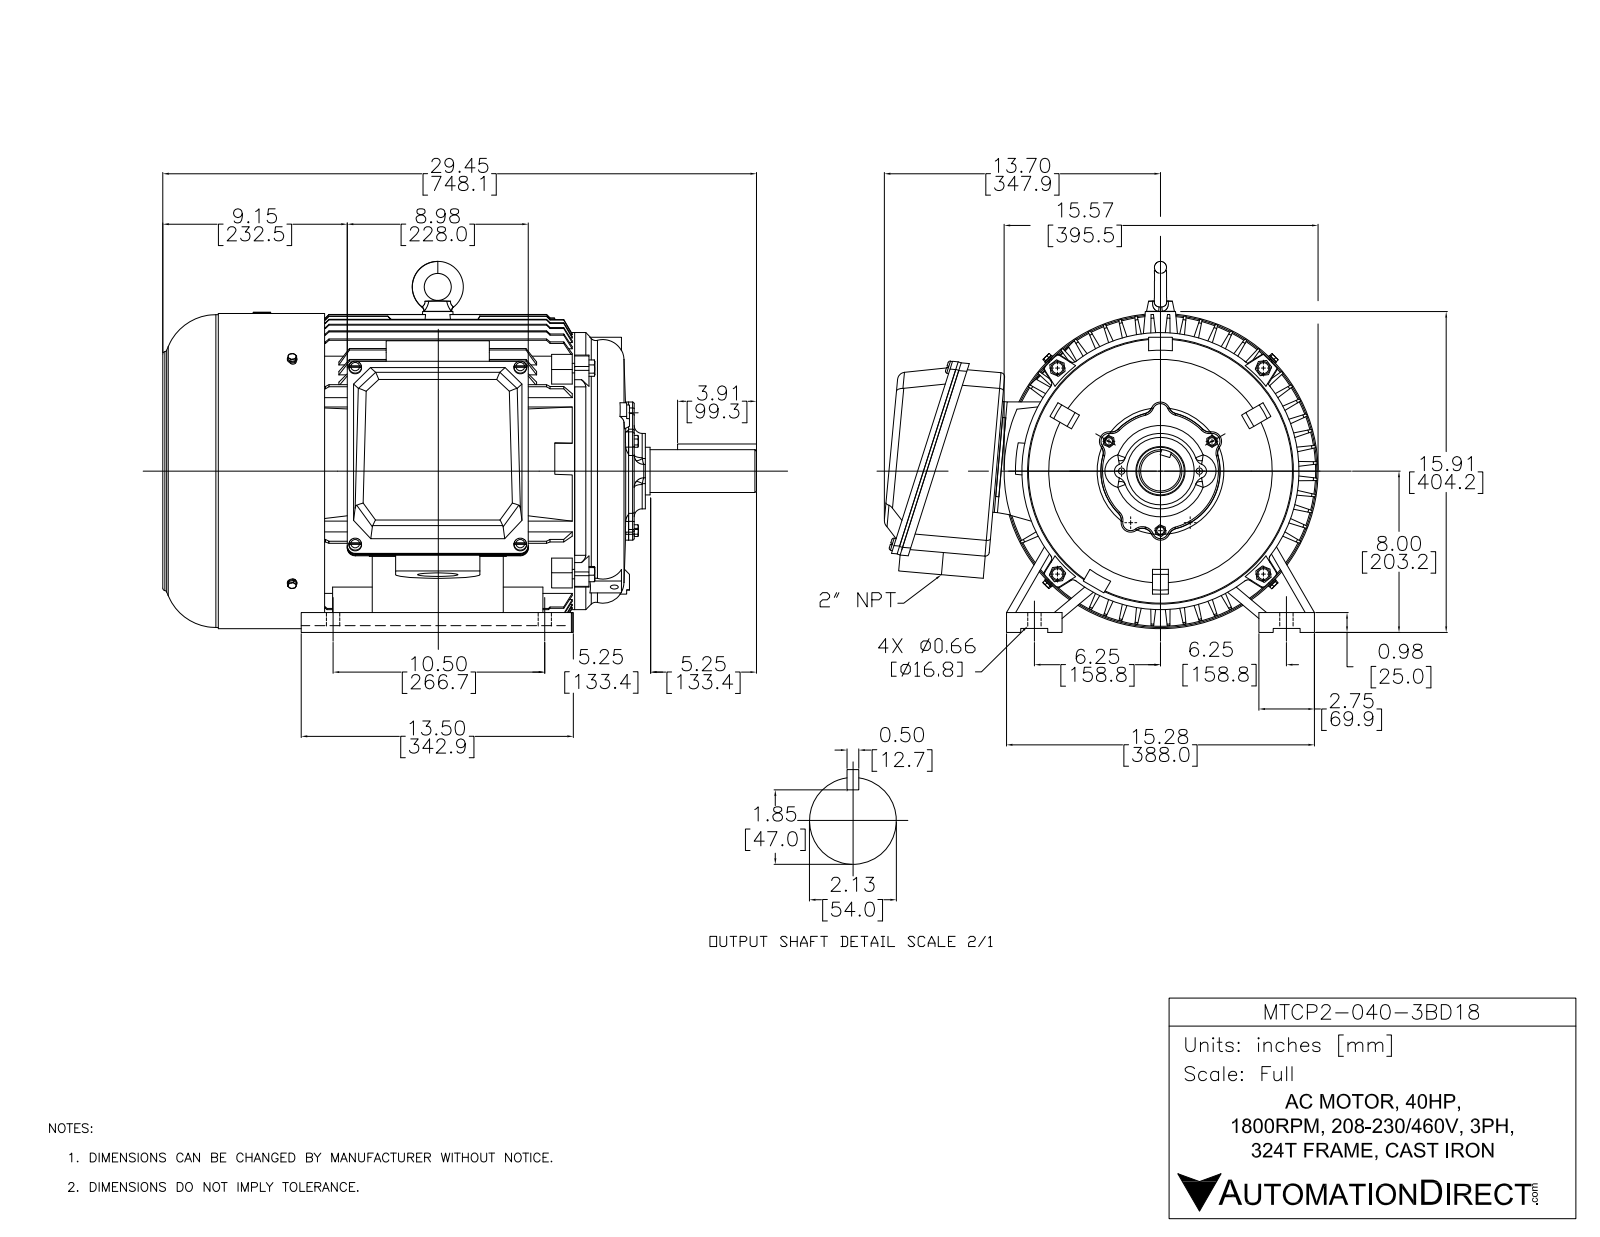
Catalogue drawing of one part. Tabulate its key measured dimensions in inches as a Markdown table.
| quantity | value |
| --- | --- |
| part name | PEWWE-324T-4,6,8 |
| STEP written by | SolidWorks 2017 (AUTOMOTIVE_DESIGN) |
| units | inches |
| bodies | 33 solids, 3018 faces (2025 planar, 564 cylindrical, 429 other) |
| overall size | 29.451 × 21.512 × 18.402 |
| volume | 2 418 in³ |
| surface area | 5 297 in² |
| round holes (diameter × count) | 0.394 × 22, 0.315 × 6, 0.252 × 4, 0.268 × 4, 0.472 × 4, 0.48 × 4, 0.539 × 4, 0.591 × 4, 0.669 × 4, 0.362 × 3, 0.748 × 2, 0.398 × 1 |
| round bosses / shafts (diameter × count) | 0.472 × 4, 0.236 × 4, 0.283 × 3, 0.428 × 2, 0.428 × 2, 15.63 × 1, 15.512 × 1, 13.74 × 1 |
| partial cylindrical surfaces (radius × count) | 0.472 × 32, 0.394 × 20, 0.157 × 15, 0.197 × 8, 0.315 × 8, 0.787 × 4, 0.354 × 2, 1.476 × 1 |
| main face-to-face distances | 0.157, 13.583, 20.315, 6.732, 0.059, 20.374, 6.791, 0.394, 0.197, 2.677 |
| hole center spacings | 3.937, 2.953, 3.527, 5.568, 5.704, 10.217, 5.114, 6.017 |
